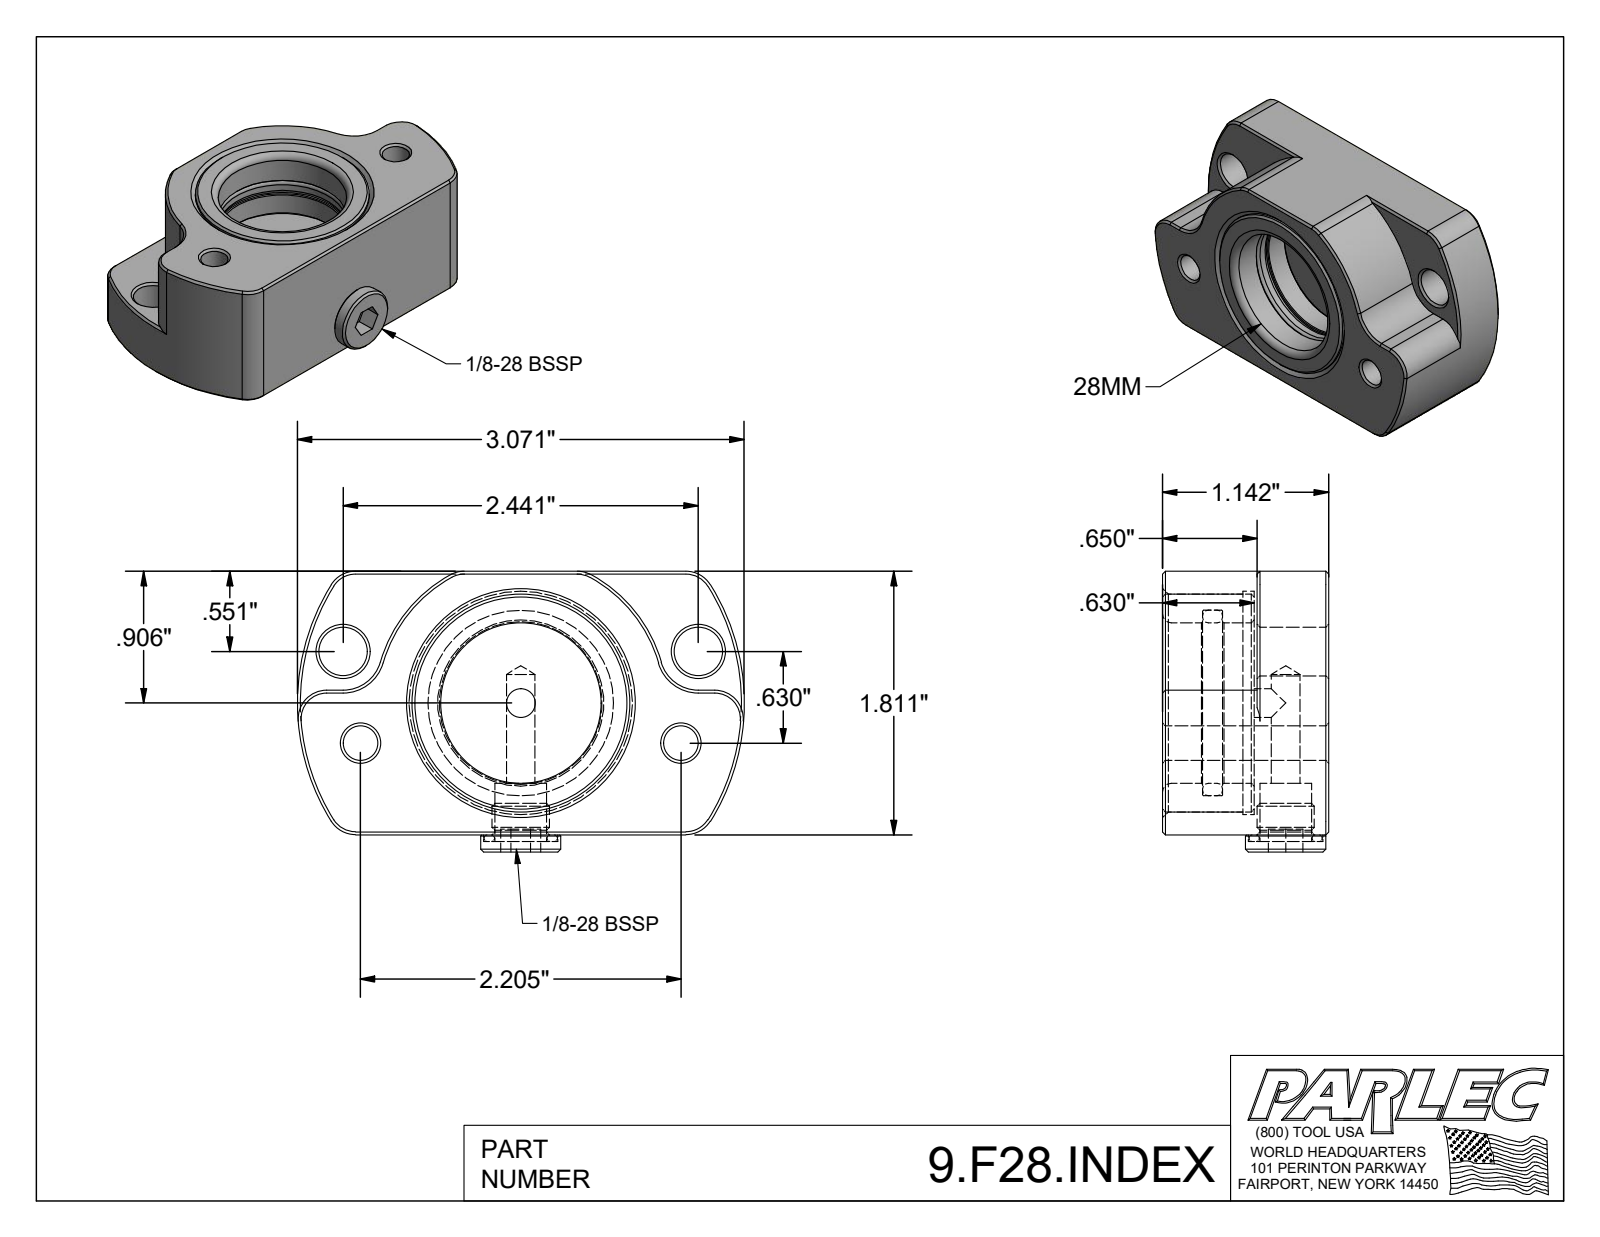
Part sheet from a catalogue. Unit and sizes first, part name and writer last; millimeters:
Units: millimetres
Overall size (bounding box): 78 × 49 × 29
Round holes (diameter × count): ⌀5 ×2, ⌀6 ×2, ⌀8.5 ×2, ⌀9 ×1, ⌀9.2 ×1, ⌀13 ×1, ⌀28 ×1, ⌀32.4 ×1, ⌀38 ×1, ⌀39 ×1
Round bosses / shafts (diameter × count): ⌀14 ×1, ⌀12.8 ×1, ⌀10 ×1
Partial cylindrical surfaces — rounded edges, fillets, slot ends (radius × count): R5 ×8, R6.75 ×2, R25.53 ×1, R39 ×1
Main face-to-face distances: 29, 13, 16, 46, 12.5, 0.5, 16.5, 3.5, 5.5, 7
Hole centre spacings: 16.28, 28.86, 32.28, 61.13, 56, 62
Volume: 73 401 mm³ · Surface area: 23 377 mm²
Bodies: 4 solids, 128 faces (39 planar, 36 cylindrical, 53 other)
Part name (STEP PRODUCT): 9.F28.INDEX; 9G28INDEX1; 9G28INDEX2; OR_3112_AF0 (+1 more)
STEP written by: Autodesk Inventor 2020 (AUTOMOTIVE_DESIGN)
